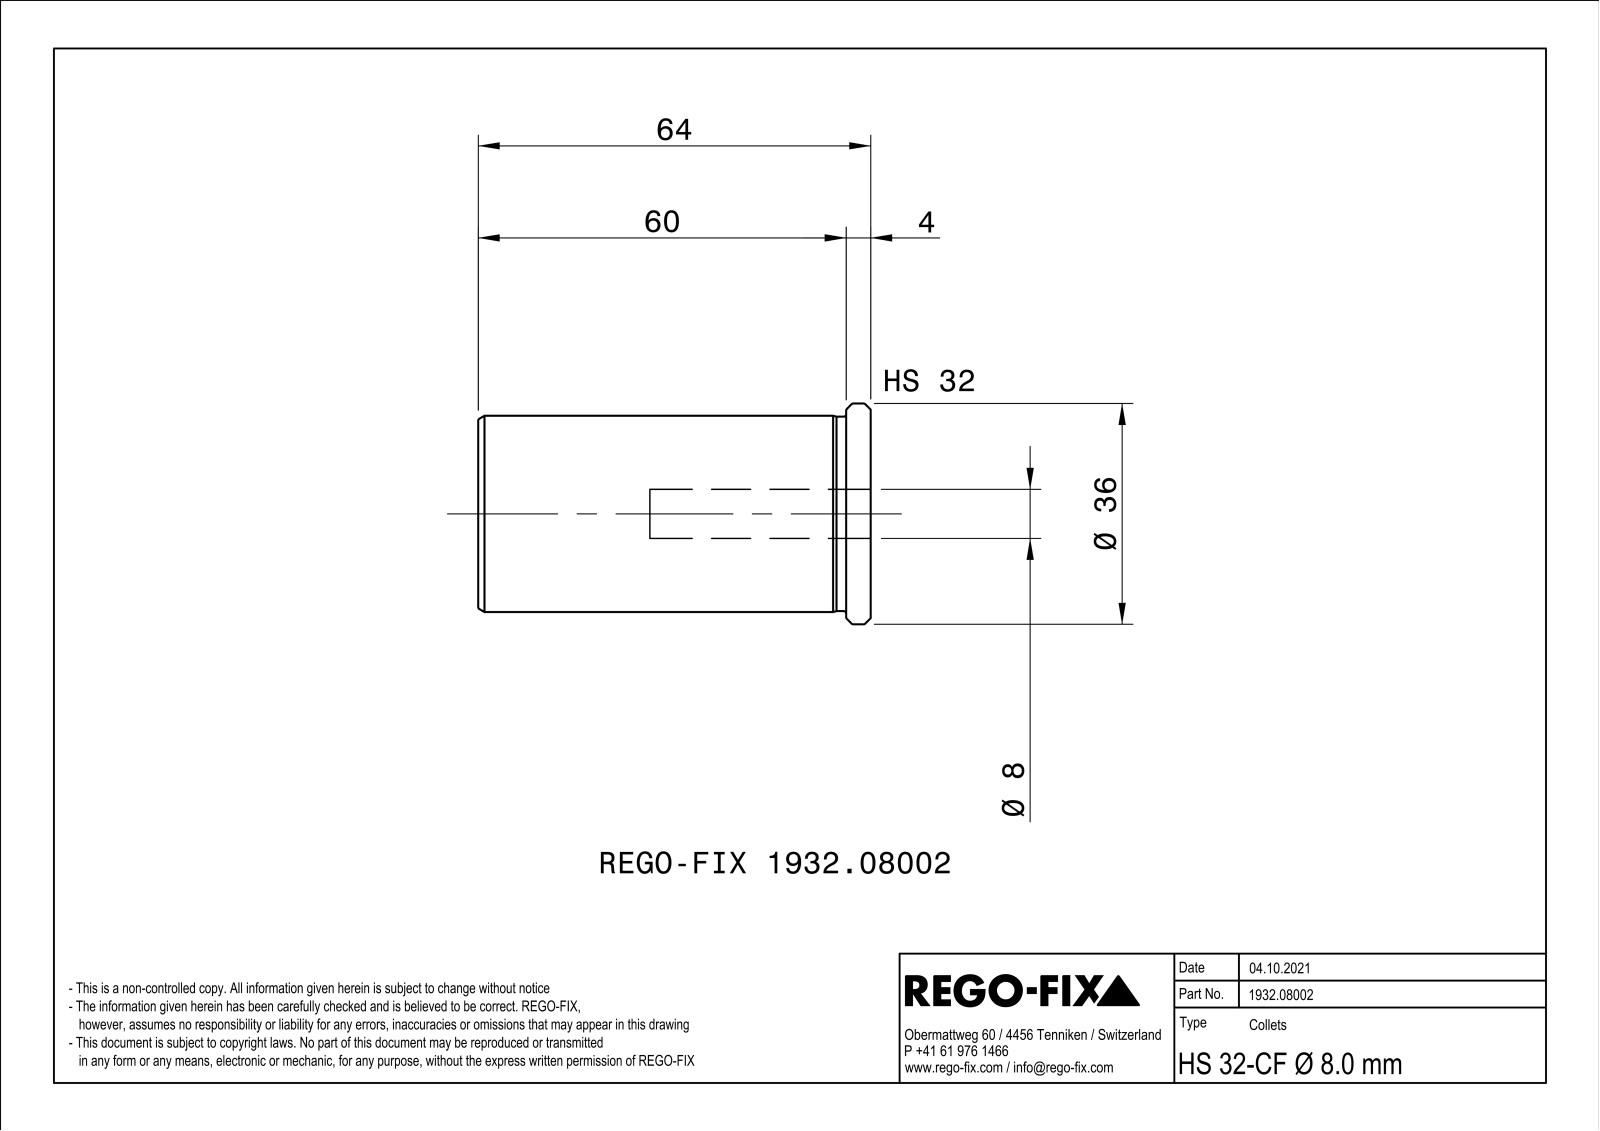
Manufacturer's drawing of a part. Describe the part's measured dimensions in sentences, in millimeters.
The part is named "NOCUT". Its 3-D file was written by "SIEMENS PLM Software Solid Edge ST10 (AUTOMOTIVE_DESIGN)". It is 1 solid with 88 faces: 14 planar, 30 cylindrical and 44 other. Overall it measures 64 by 35.99 by 35.99 millimeters. Its volume is 38 500 cubic millimeters and its surface area 14 794 square millimeters. Round holes: 1 of diameter 10, 1 of diameter 26.5. Round bosses or shafts: 1 of diameter 36, 1 of diameter 32, 1 of diameter 31.7. Partial cylindrical surfaces (rounded edges, fillets, slot ends): 6 of radius 0.5, 4 of radius 0.75, 1 of radius 4. The main face-to-face distances are 1, 64, 4, 60.
